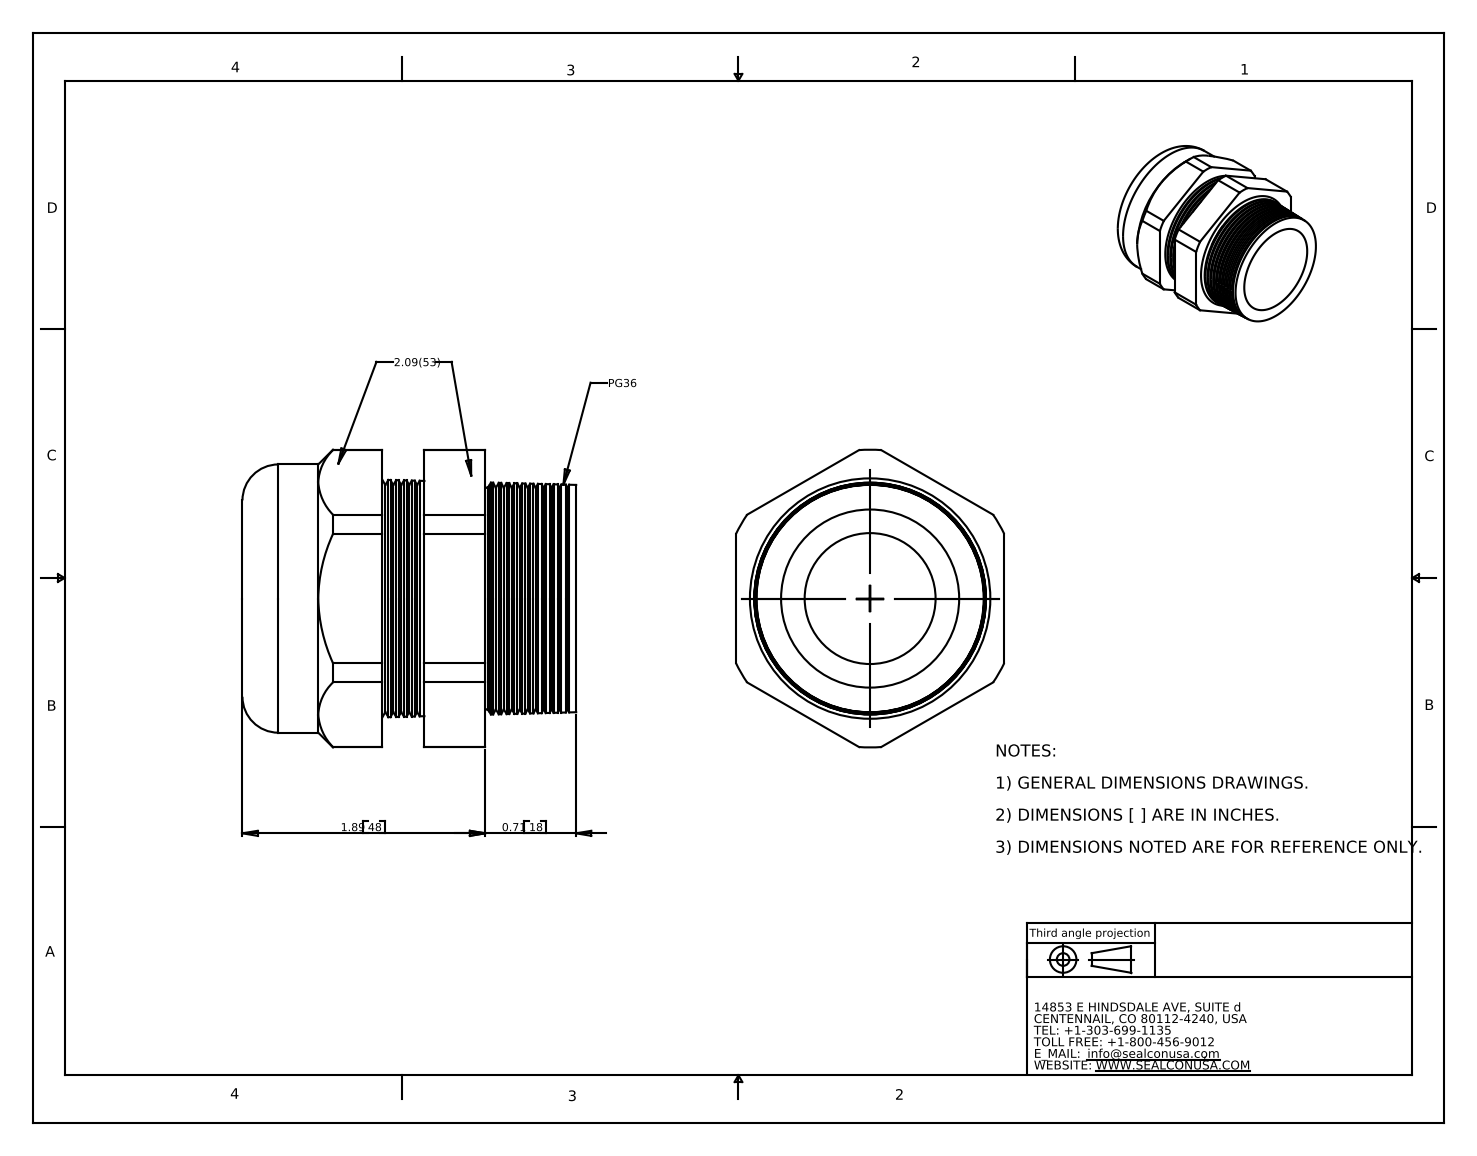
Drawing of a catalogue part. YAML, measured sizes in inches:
part_name: "CD36CR-BK"
step_written_by: "SolidWorks 2007 (CONFIG_CONTROL_DESIGN)"
units: inches
bodies: {solids: 2, faces: 158, planar: 20, cylindrical: 22, other: 116}
overall_size: [2.6, 2.32, 2.09]
volume: 5.503
surface_area: 42.14
round_holes:
  - {diameter: 1.02, count: 1}
  - {diameter: 1.387, count: 1}
round_bosses_or_shafts:
  - {diameter: 2.09, count: 1}
partial_cylinders:
  - {radius: 1.16, count: 1}
face_to_face_distances: [2.09, 0.827, 0.5, 0.327, 1.3, 0.8, 0.472, 2.009, 1.509, 1.182]
